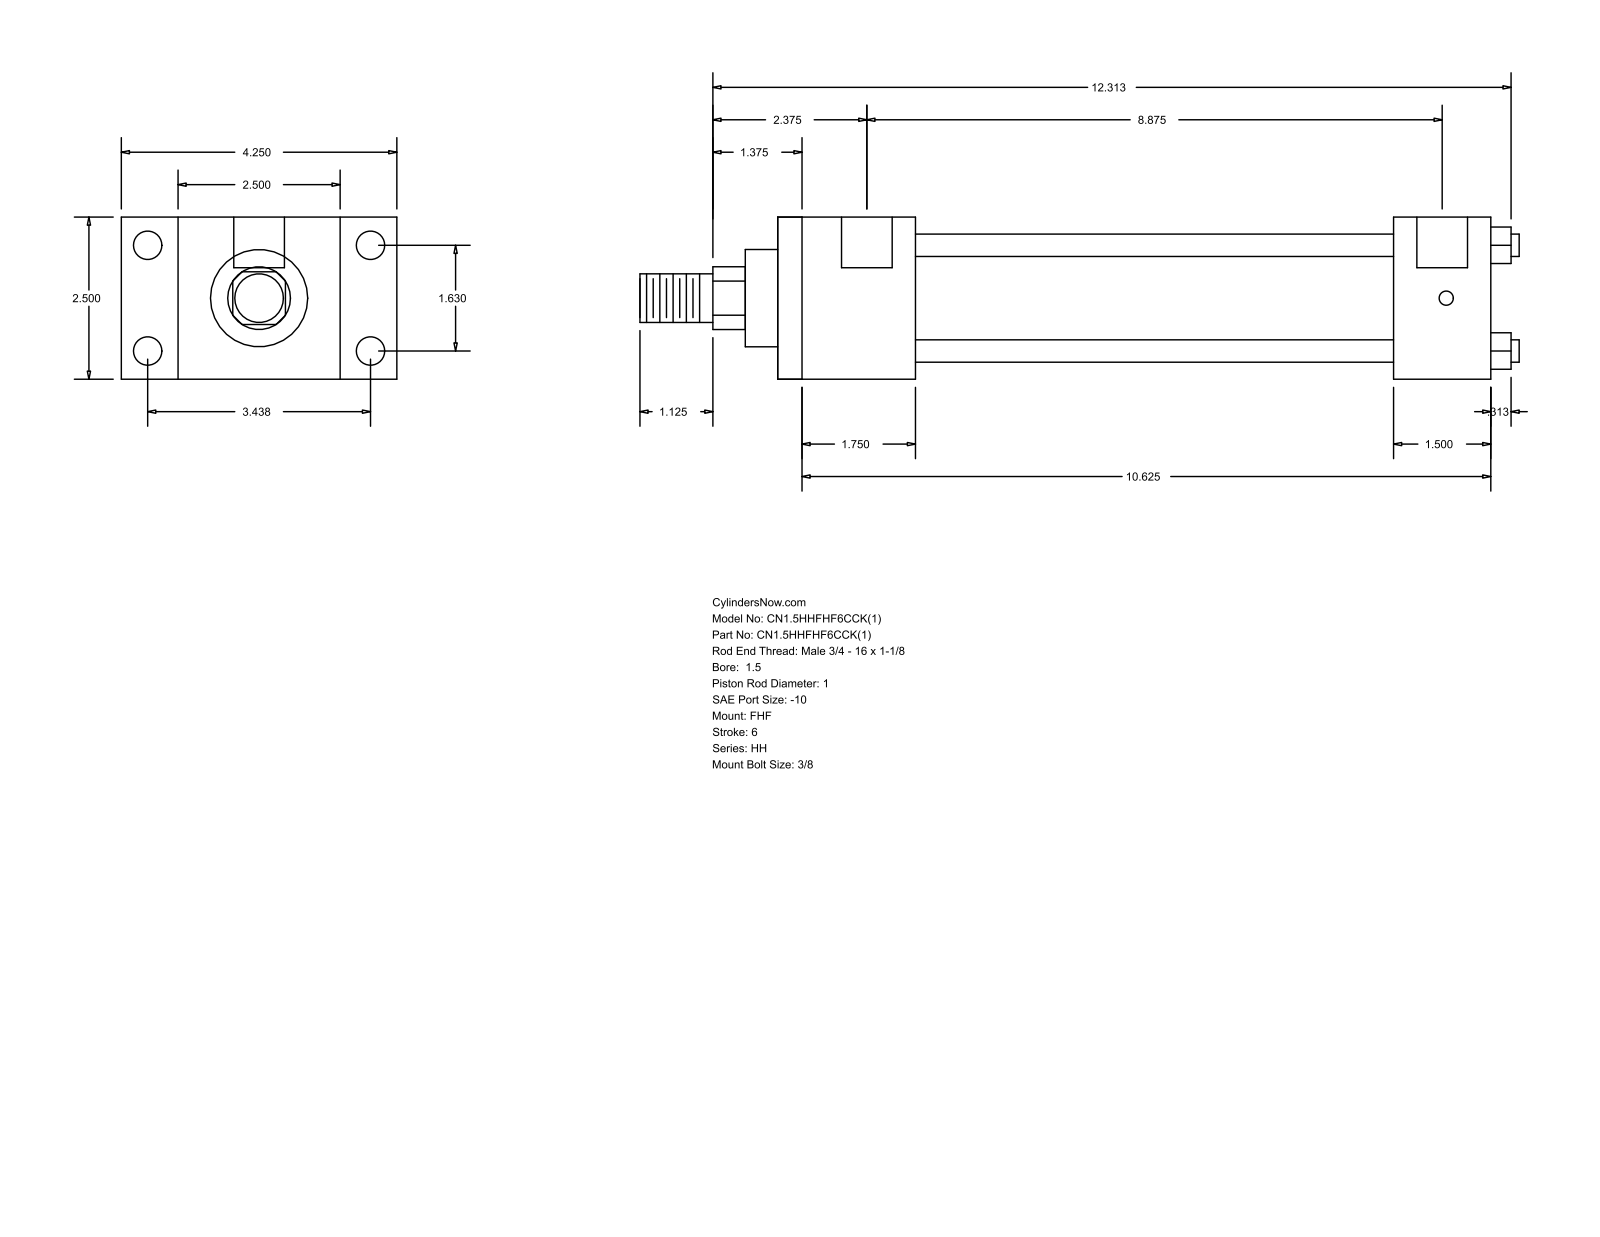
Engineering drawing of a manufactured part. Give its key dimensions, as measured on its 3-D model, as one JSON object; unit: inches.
{"part_name": "HH_FHF__0150_1", "step_written_by": "GSSL Pune (CONFIG_CONTROL_DESIGN)", "units": "inches", "bodies": {"solids": 0, "faces": 88, "planar": 60, "cylindrical": 28, "other": 0}, "overall_size": [13.563, 4.25, 2.5], "round_holes": [[0.219, 4], [0.438, 4], [0.781, 2]], "round_bosses_or_shafts": [[0.345, 4], [1.75, 1], [1.5, 1], [1, 1], [0.75, 1]], "partial_cylinders_radius": [[0.484, 1]], "face_to_face_distances": [2.5, 0.875, 3.375, 2.125, 4.25, 11, 8.875, 1.5, 9.5, 7.375], "hole_center_spacings": [0.063, 1.63, 3.438, 3.805, 8.937, 9, 8.875]}
